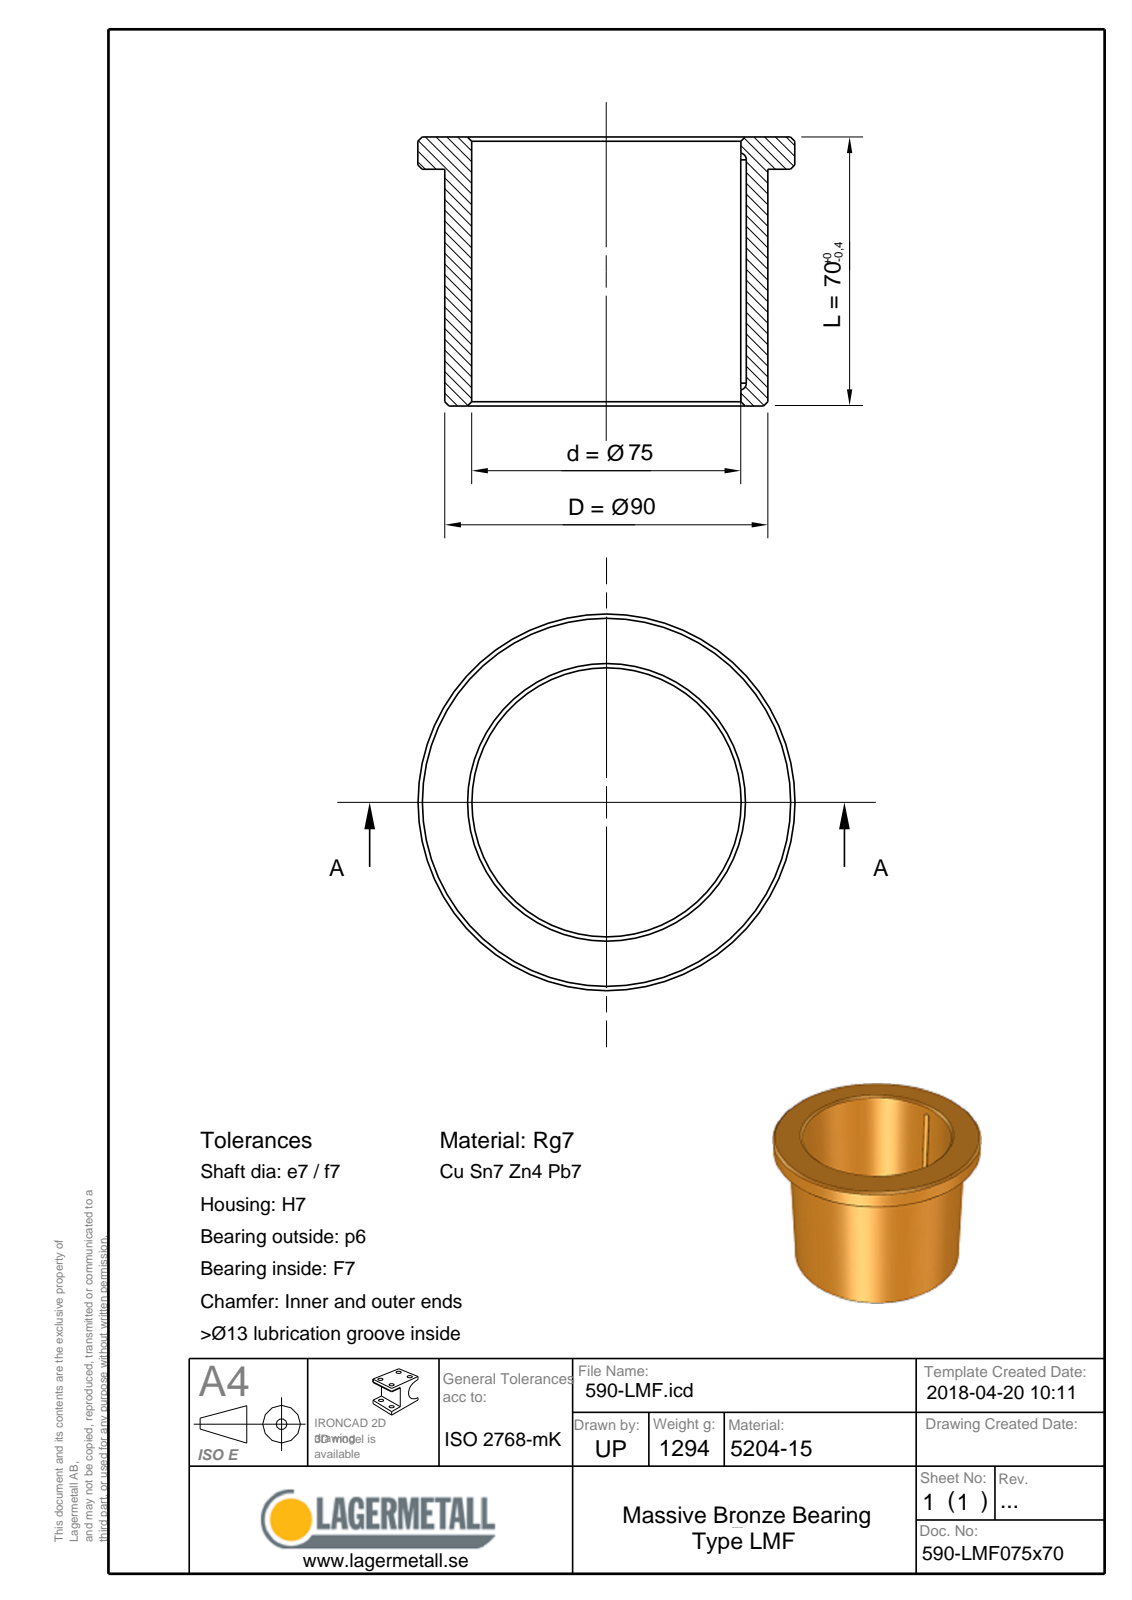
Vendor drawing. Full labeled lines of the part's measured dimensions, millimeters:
Part name (STEP PRODUCT): 590-LMF075x70
STEP written by: Spatial InterOp 3D (CONFIG_CONTROL_DESIGN)
Units: millimetres
Bodies: 1 solid, 16 faces (4 planar, 5 cylindrical, 7 other)
Overall size (bounding box): 100 × 100 × 70
Volume: 147 077 mm³ · Surface area: 42 699 mm²
Round holes (diameter × count): ⌀75 ×1
Round bosses / shafts (diameter × count): ⌀100 ×1, ⌀90 ×1
Partial cylindrical surfaces — rounded edges, fillets, slot ends (radius × count): R1.75 ×2
Main face-to-face distances: 70, 62, 8
